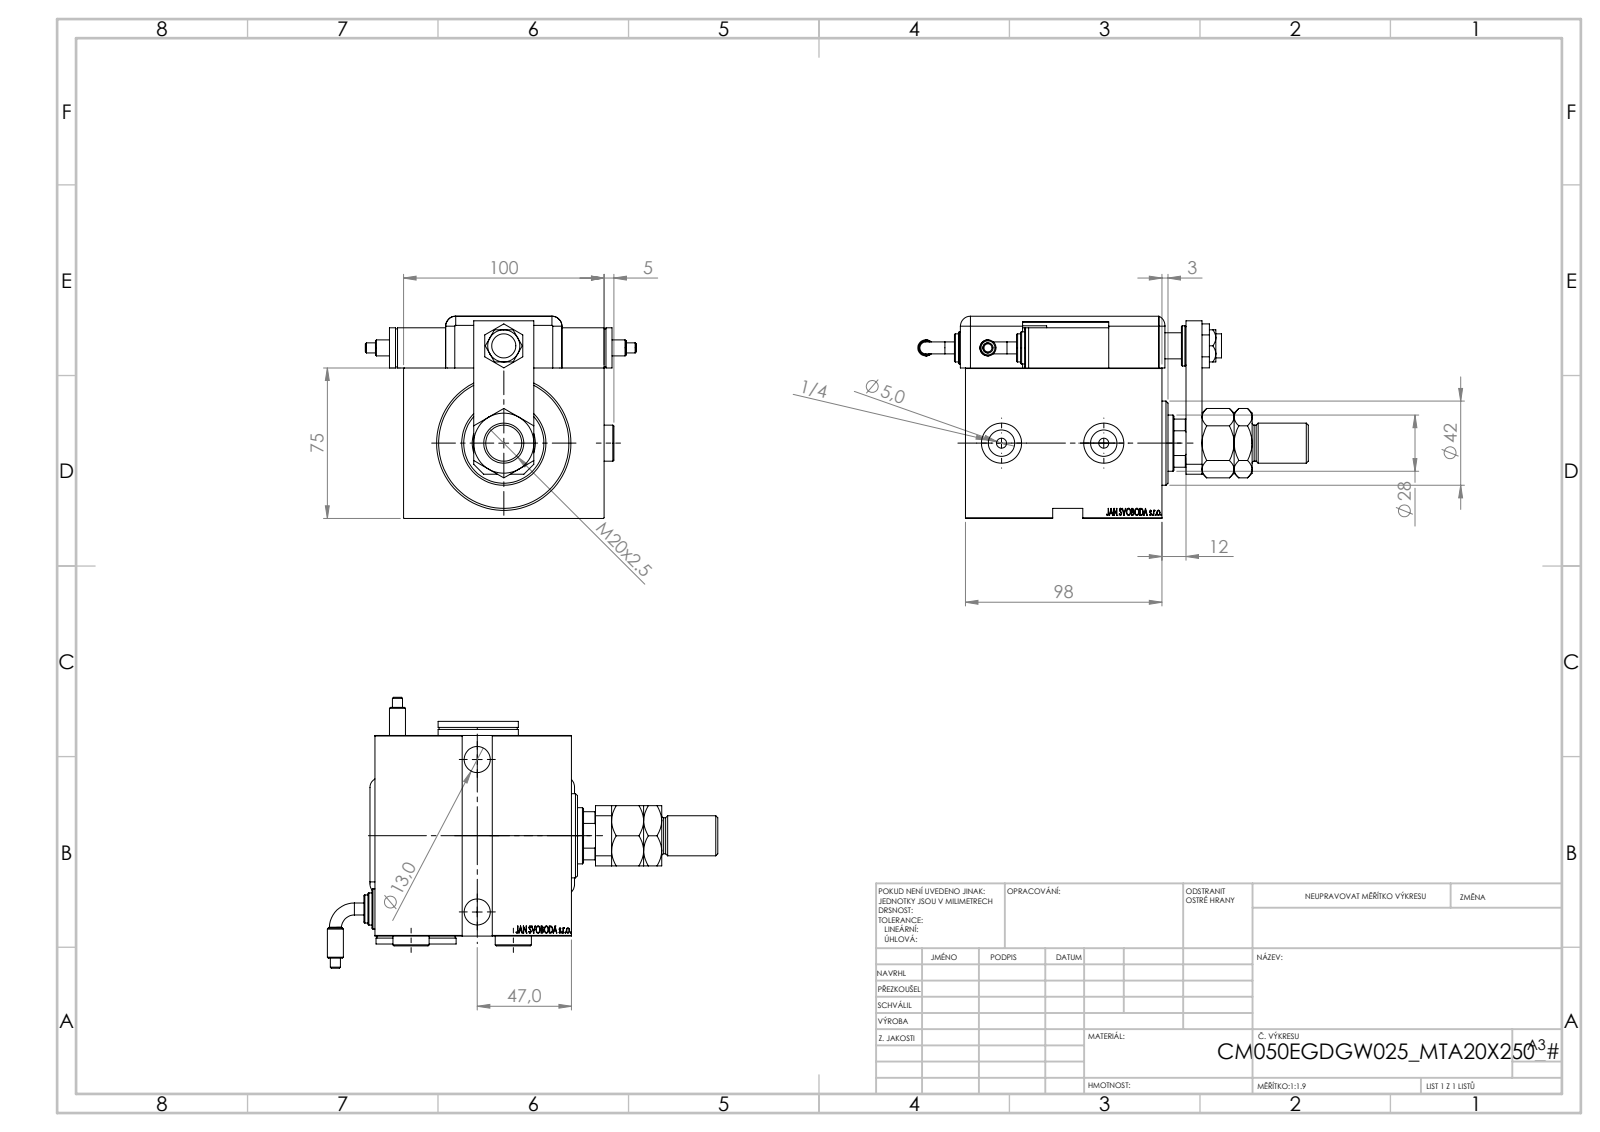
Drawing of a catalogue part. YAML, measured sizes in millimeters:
part_name: "V450CM_E_VCP; SWITCH Q; KRYT; MAGNETIC SWITCH Q (+7 more)"
step_written_by: "SolidWorks 2019 (CONFIG_CONTROL_DESIGN)"
units: millimeters
bodies: {solids: 16, faces: 1363, planar: 669, cylindrical: 127, other: 567}
overall_size: [194.76, 135.01, 100.8]
volume: 843683
surface_area: 162417
round_holes:
  - {diameter: 13, count: 3}
  - {diameter: 20, count: 3}
  - {diameter: 4, count: 2}
  - {diameter: 5, count: 2}
  - {diameter: 8, count: 2}
  - {diameter: 13.16, count: 2}
  - {diameter: 19, count: 2}
  - {diameter: 12, count: 1}
  - {diameter: 14, count: 1}
  - {diameter: 18.5, count: 1}
  - {diameter: 28, count: 1}
  - {diameter: 31.5, count: 1}
round_bosses_or_shafts:
  - {diameter: 20, count: 3}
  - {diameter: 18, count: 3}
  - {diameter: 16, count: 2}
  - {diameter: 14, count: 2}
  - {diameter: 8, count: 2}
  - {diameter: 6, count: 2}
  - {diameter: 5.04, count: 2}
  - {diameter: 52, count: 1}
partial_cylinders:
  - {radius: 5, count: 9}
  - {radius: 10, count: 1}
  - {radius: 13.5, count: 1}
face_to_face_distances: [3, 75, 98, 100, 14, 20, 84, 79, 25, 100.8]
hole_center_spacings: [47.2, 61.22, 20, 48.5, 51, 76]
